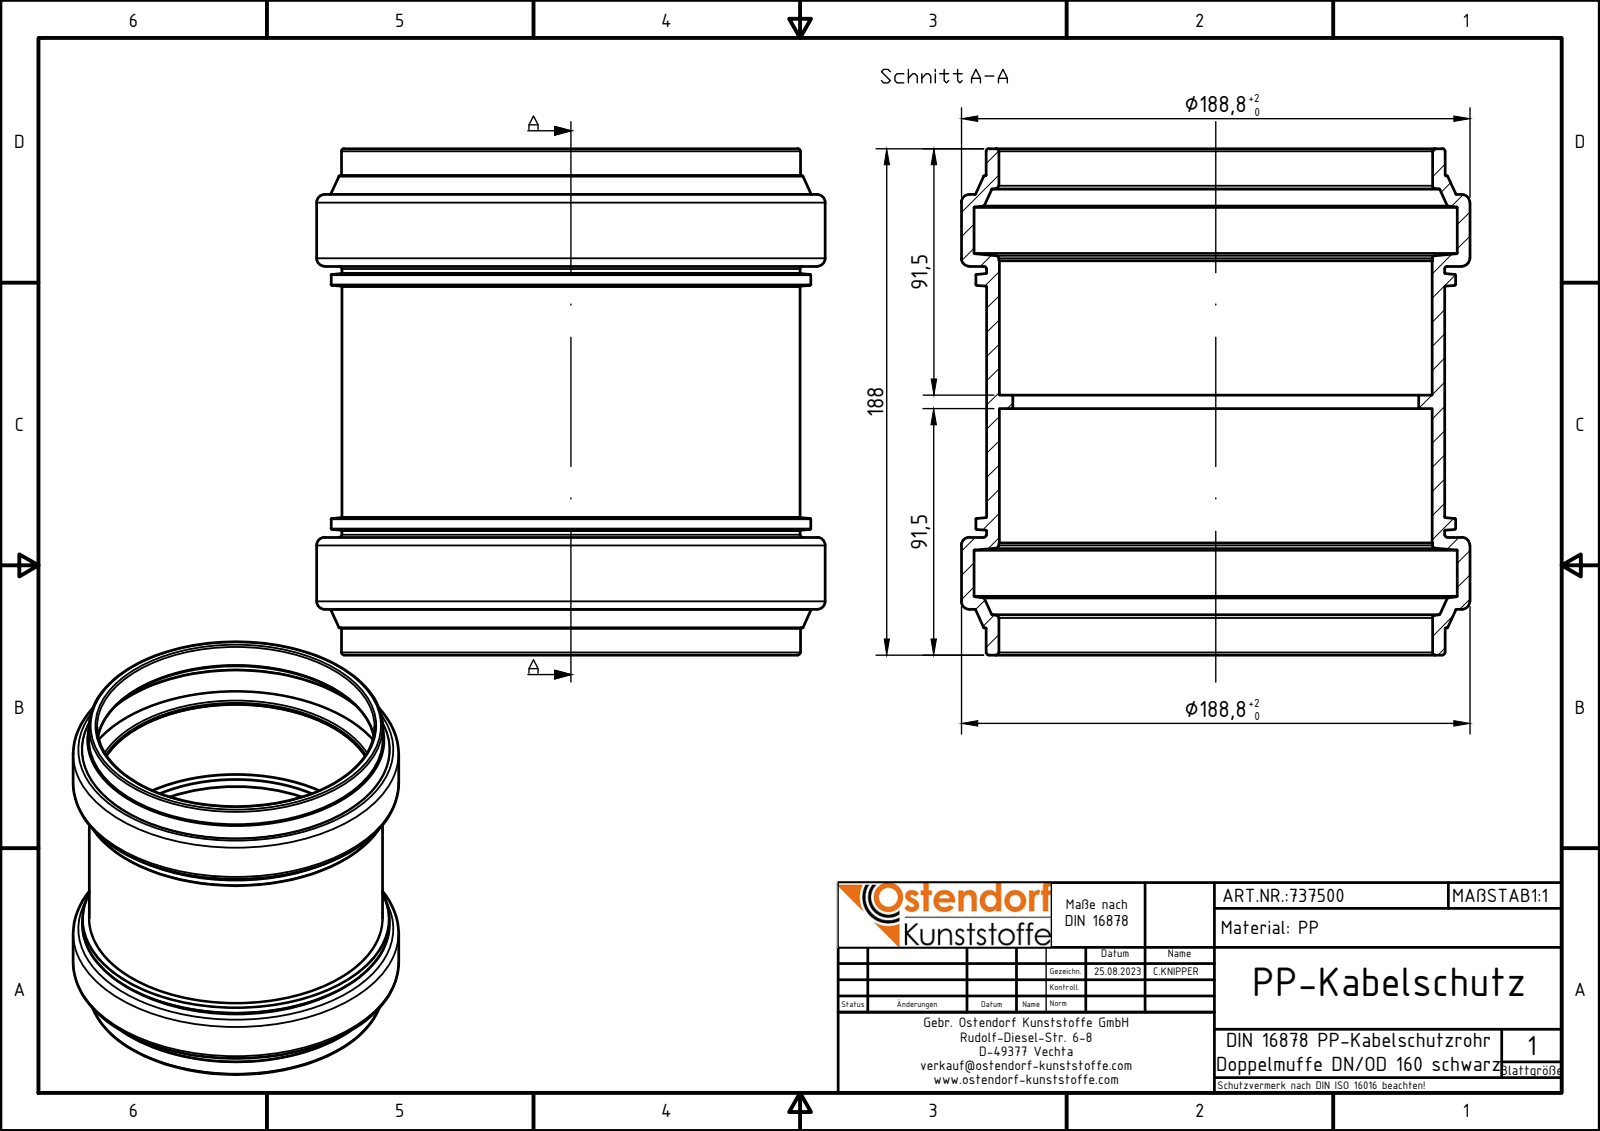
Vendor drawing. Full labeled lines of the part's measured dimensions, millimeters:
Part name (STEP PRODUCT): 737500z
STEP written by: Autodesk Inventor 2024 (AUTOMOTIVE_DESIGN)
Units: millimetres
Bodies: 1 solid, 80 faces (12 planar, 18 cylindrical, 50 other)
Overall size (bounding box): 188.8 × 188.8 × 188
Volume: 577 176 mm³ · Surface area: 247 094 mm²
Round holes (diameter × count): ⌀150.7 ×1, ⌀160.7 ×1, ⌀161 ×1, ⌀179.4 ×1
Round bosses / shafts (diameter × count): ⌀188.8 ×1, ⌀178.1 ×1, ⌀170.4 ×1, ⌀170.1 ×1
Main face-to-face distances: 47.8, 52.8, 100.6, 43.7, 91.5, 96.5, 144.3, 5, 17, 171
